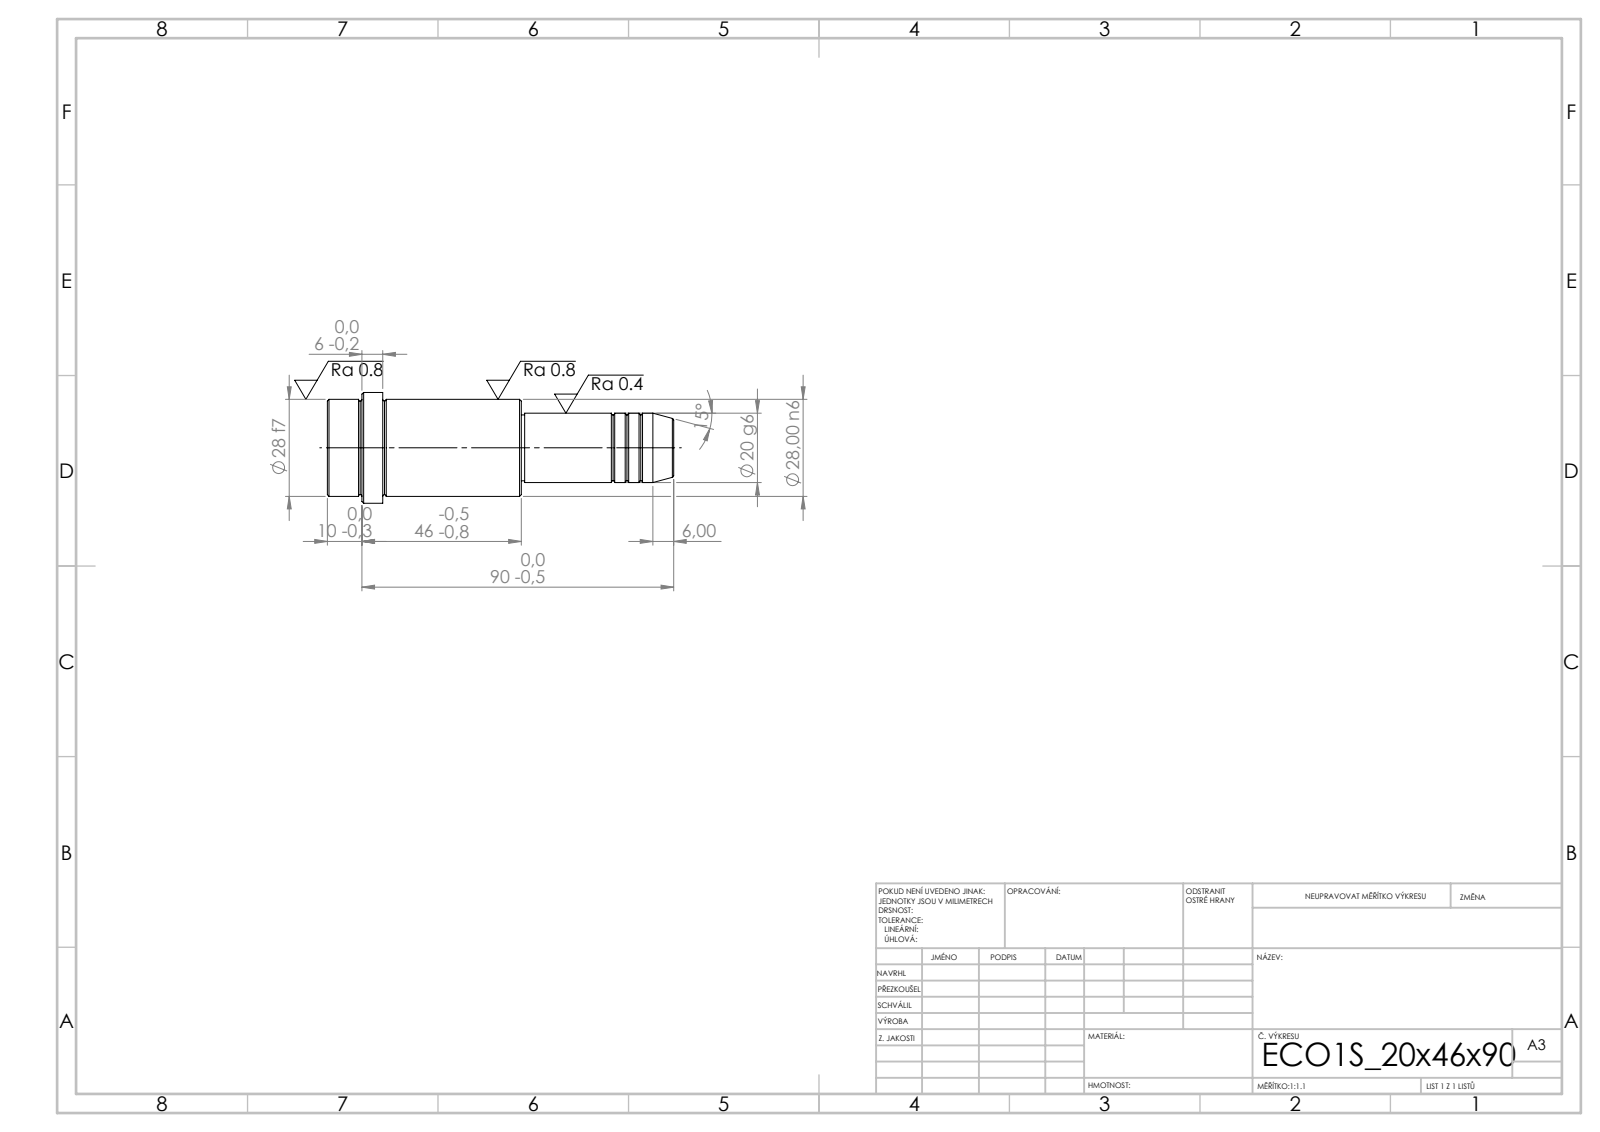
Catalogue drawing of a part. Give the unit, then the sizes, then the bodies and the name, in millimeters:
Units: millimetres
Overall size (bounding box): 100 × 32 × 32
Round bosses / shafts (diameter × count): ⌀32 ×1, ⌀28 ×1, ⌀20 ×1, ⌀19 ×1
Main face-to-face distances: 56, 44, 100, 84, 40, 16, 90, 46, 6, 10
Volume: 48 943 mm³ · Surface area: 9 426 mm²
Bodies: 1 solid, 52 faces (6 planar, 16 cylindrical, 30 other)
STEP written by: SolidWorks 2019 (CONFIG_CONTROL_DESIGN)
